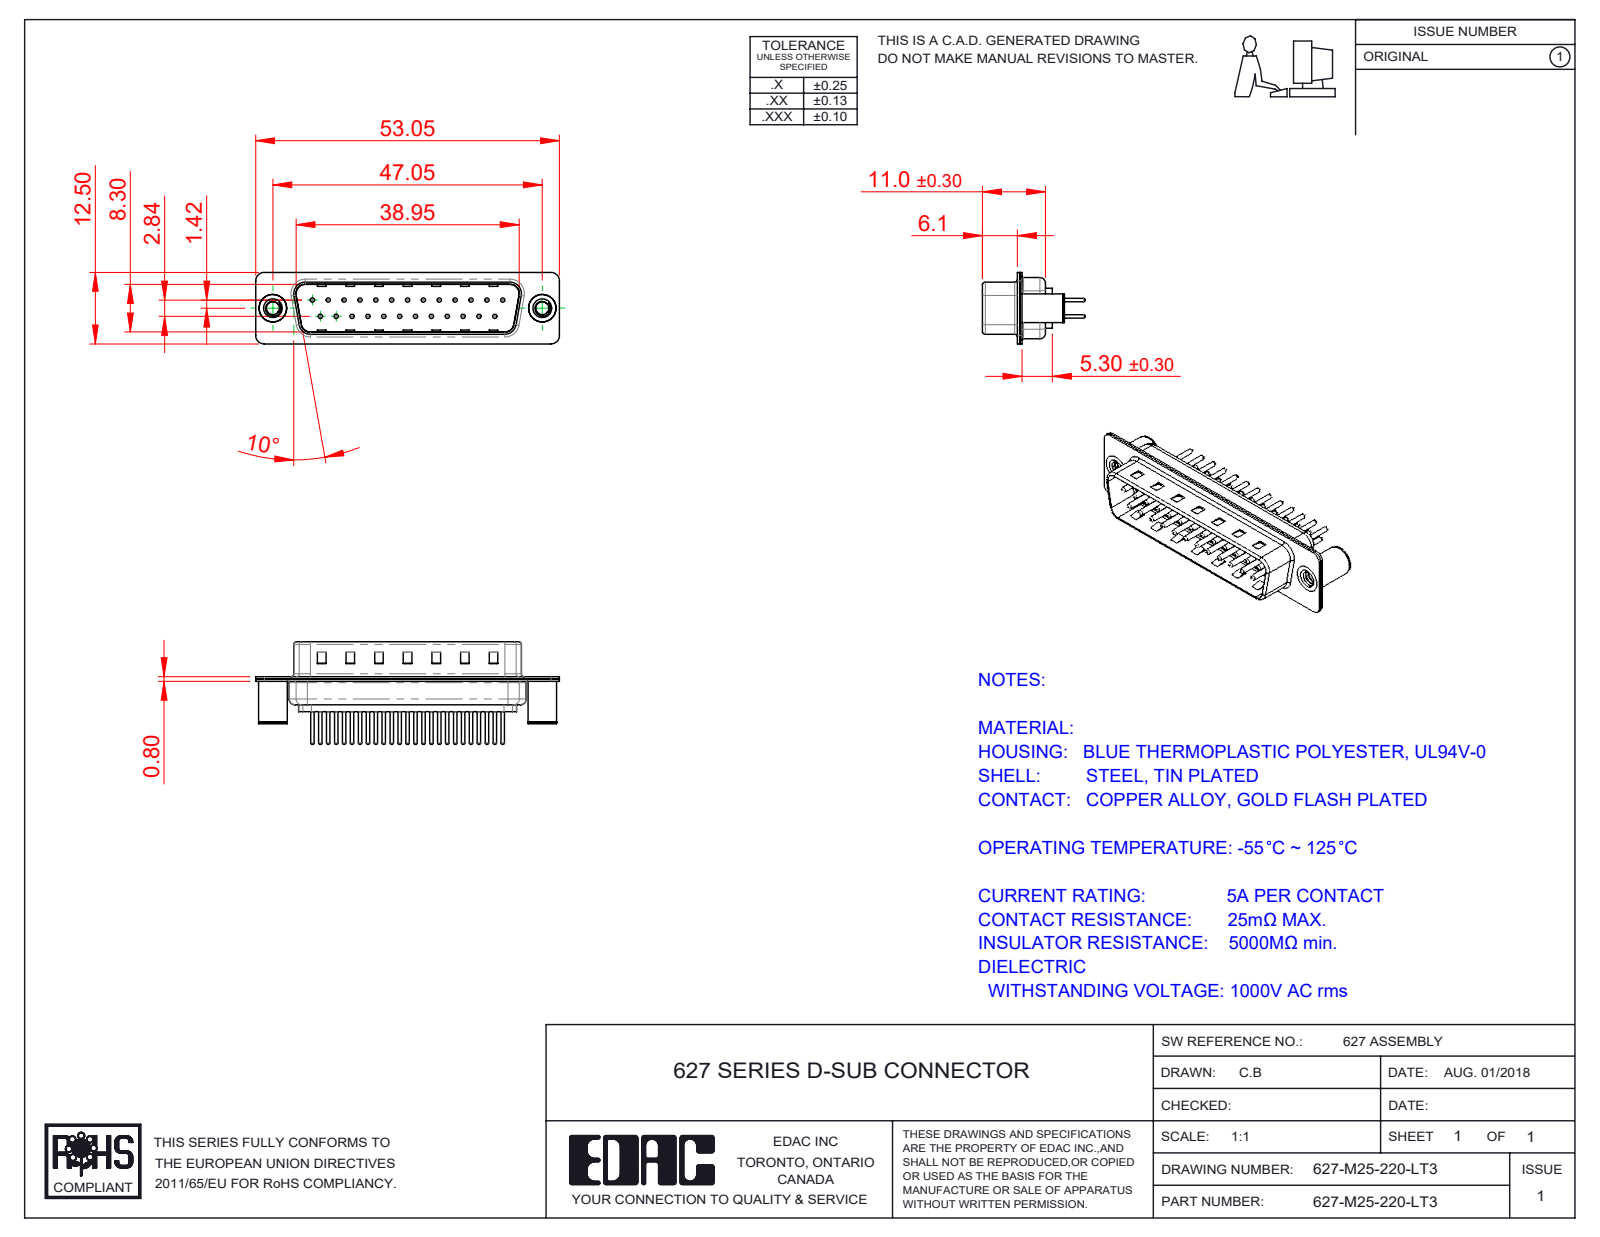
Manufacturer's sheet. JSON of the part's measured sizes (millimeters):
{"part_name": "627M Shell Front_25 Contacts; 627M Housing_25 Contacts; 627M Shell Rear_25 Contacts; 627M Contact Row 1_20 (+3 more)", "step_written_by": "SolidWorks 2020 (CONFIG_CONTROL_DESIGN)", "units": "millimeters", "bodies": {"solids": 30, "faces": 1335, "planar": 346, "cylindrical": 511, "other": 478}, "overall_size": [53.05, 17.9, 12.5], "volume_mm3": 2842, "surface_area_mm2": 7101, "round_holes": [[0.75, 25], [1.6, 25], [2, 25], [2.26, 2], [3.26, 2], [4, 2], [4.8, 2]], "round_bosses_or_shafts": [[1.5, 25], [0.6, 25], [5, 2], [4.9, 2]], "partial_cylinders_radius": [[1.5, 16], [2, 12], [0.5, 8], [1.6, 8], [0.25, 4], [0.6, 4], [0.65, 4], [0.9, 4]], "face_to_face_distances": [0.4, 0.8, 9.5, 9.1, 8.7, 9.9, 1.2, 6.1, 5.7, 0.75], "hole_center_spacings": [3.16, 2.77, 5.54, 8.31, 11.08, 13.85, 16.62, 5.03]}
